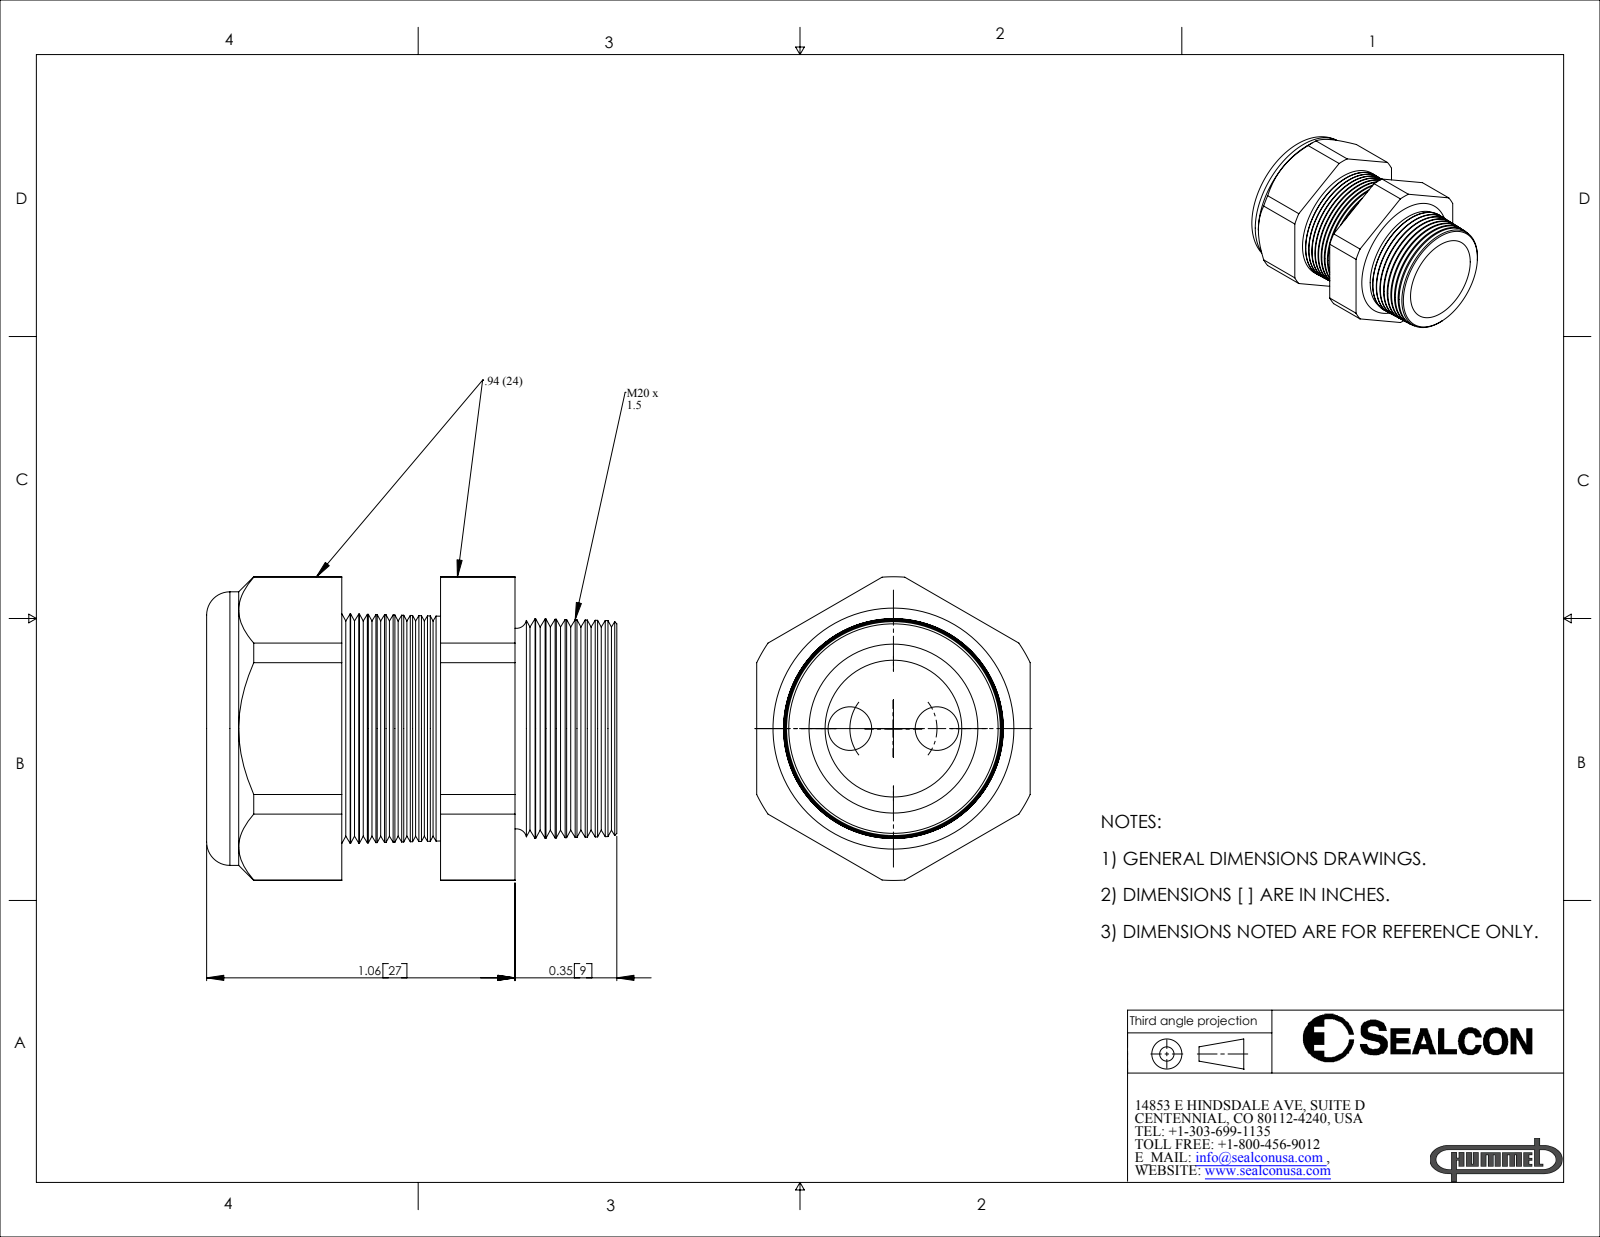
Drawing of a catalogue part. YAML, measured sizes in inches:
part_name: "CD20M7-GY"
step_written_by: "SolidWorks 2007 (CONFIG_CONTROL_DESIGN)"
units: inches
bodies: {solids: 2, faces: 178, planar: 20, cylindrical: 24, other: 134}
overall_size: [1.41, 1.043, 0.94]
volume: 0.577
surface_area: 9.887
round_holes:
  - {diameter: 0.15, count: 2}
  - {diameter: 0.45, count: 1}
  - {diameter: 0.47, count: 1}
round_bosses_or_shafts:
  - {diameter: 0.94, count: 1}
partial_cylinders:
  - {radius: 0.522, count: 1}
face_to_face_distances: [0.94, 0.804, 0.465, 0.34, 1.06, 0.596, 0.256, 1.41, 0.946, 0.606]
hole_center_spacings: [0.15, 0.299]
